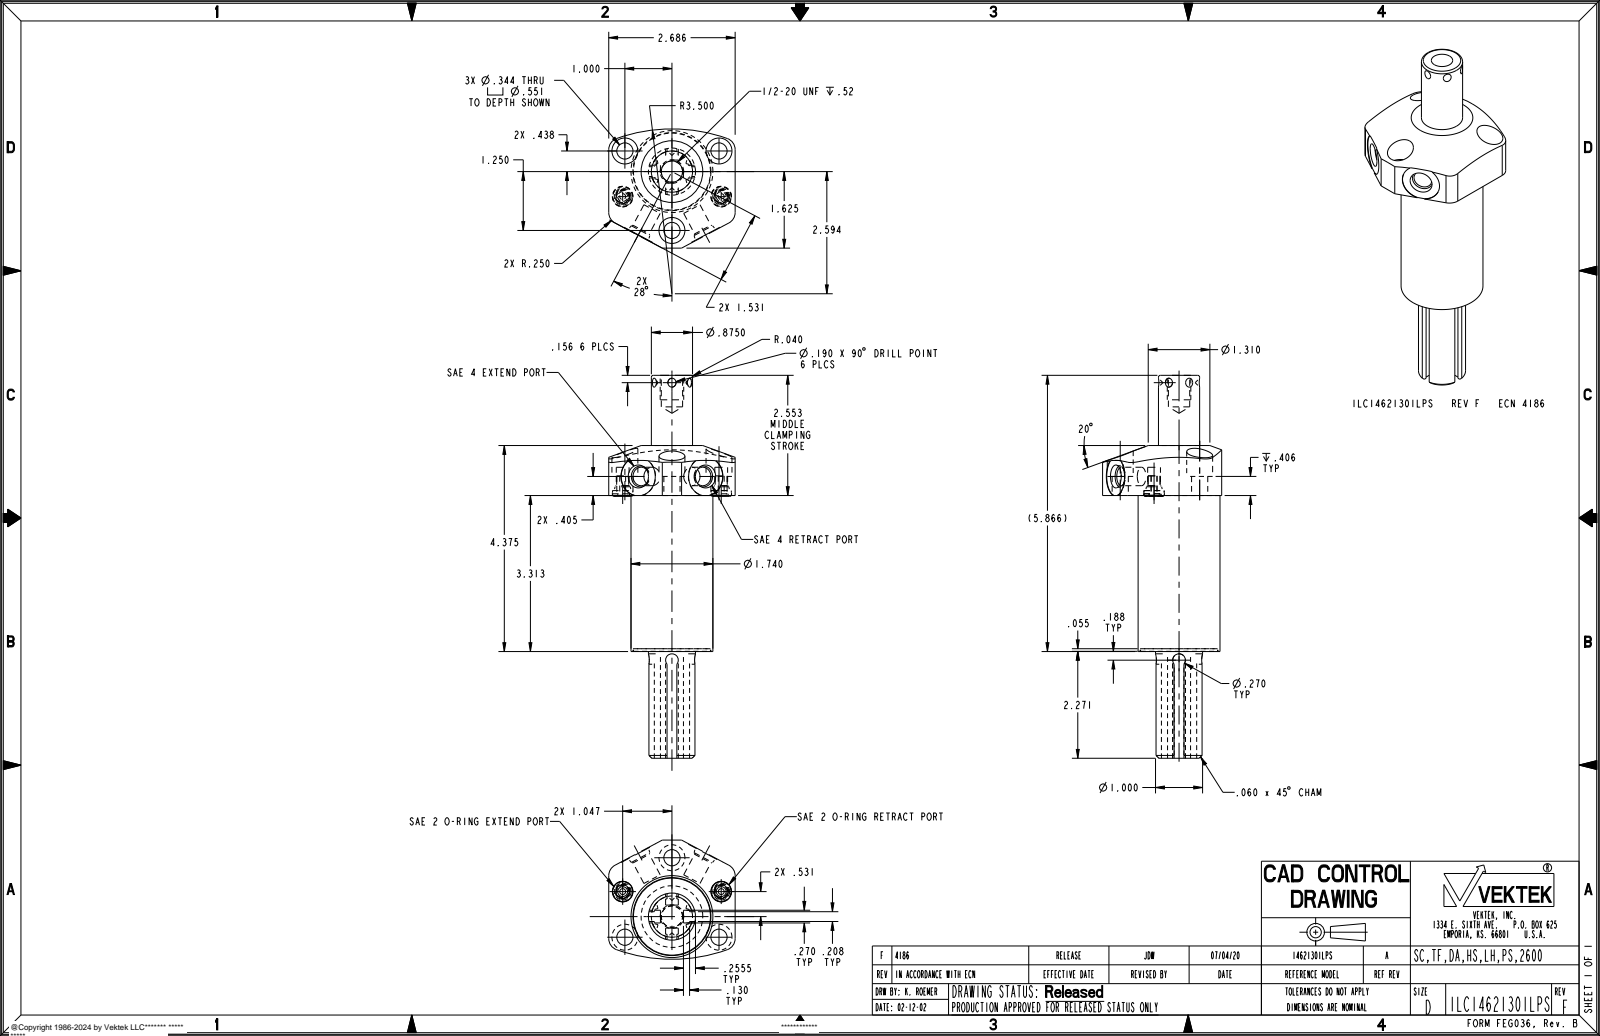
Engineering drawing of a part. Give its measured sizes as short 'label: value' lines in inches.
name: ILC14621301LPS
written by: PRO/ENGINEER BY PARAMETRIC TECHNOLOGY CORPORATION, 2013320 (AUTOMOTIVE_DESIGN)
unit: in
bodies: 1 solid, 177 faces (64 planar, 67 cylindrical, 46 other)
size: 8.132 × 2.686 × 2.531
volume: 14.71 in³; area: 63.43 in²
holes: 3× ⌀0.344, 3× ⌀0.551, 2× ⌀0.125, 2× ⌀0.272, 2× ⌀0.392, 2× ⌀0.438, 1× ⌀0.453, 1× ⌀1.656
bosses: 2× ⌀0.43, 2× ⌀0.256, 2× ⌀0.21, 1× ⌀1.74, 1× ⌀1.636, 1× ⌀1, 1× ⌀0.875, 1× ⌀0.5
rounds: 4× R0.25, 2× R0.135, 2× R0.412, 1× R3.5
face distances: 0.109, 0.38, 0.141, 0.348, 0.031, 0.239, 3.308, 1.098, 1.587, 0.489
hole spacings: 0.97, 1.092, 1.174, 1.27, 1.962, 2.265, 1.25, 2
